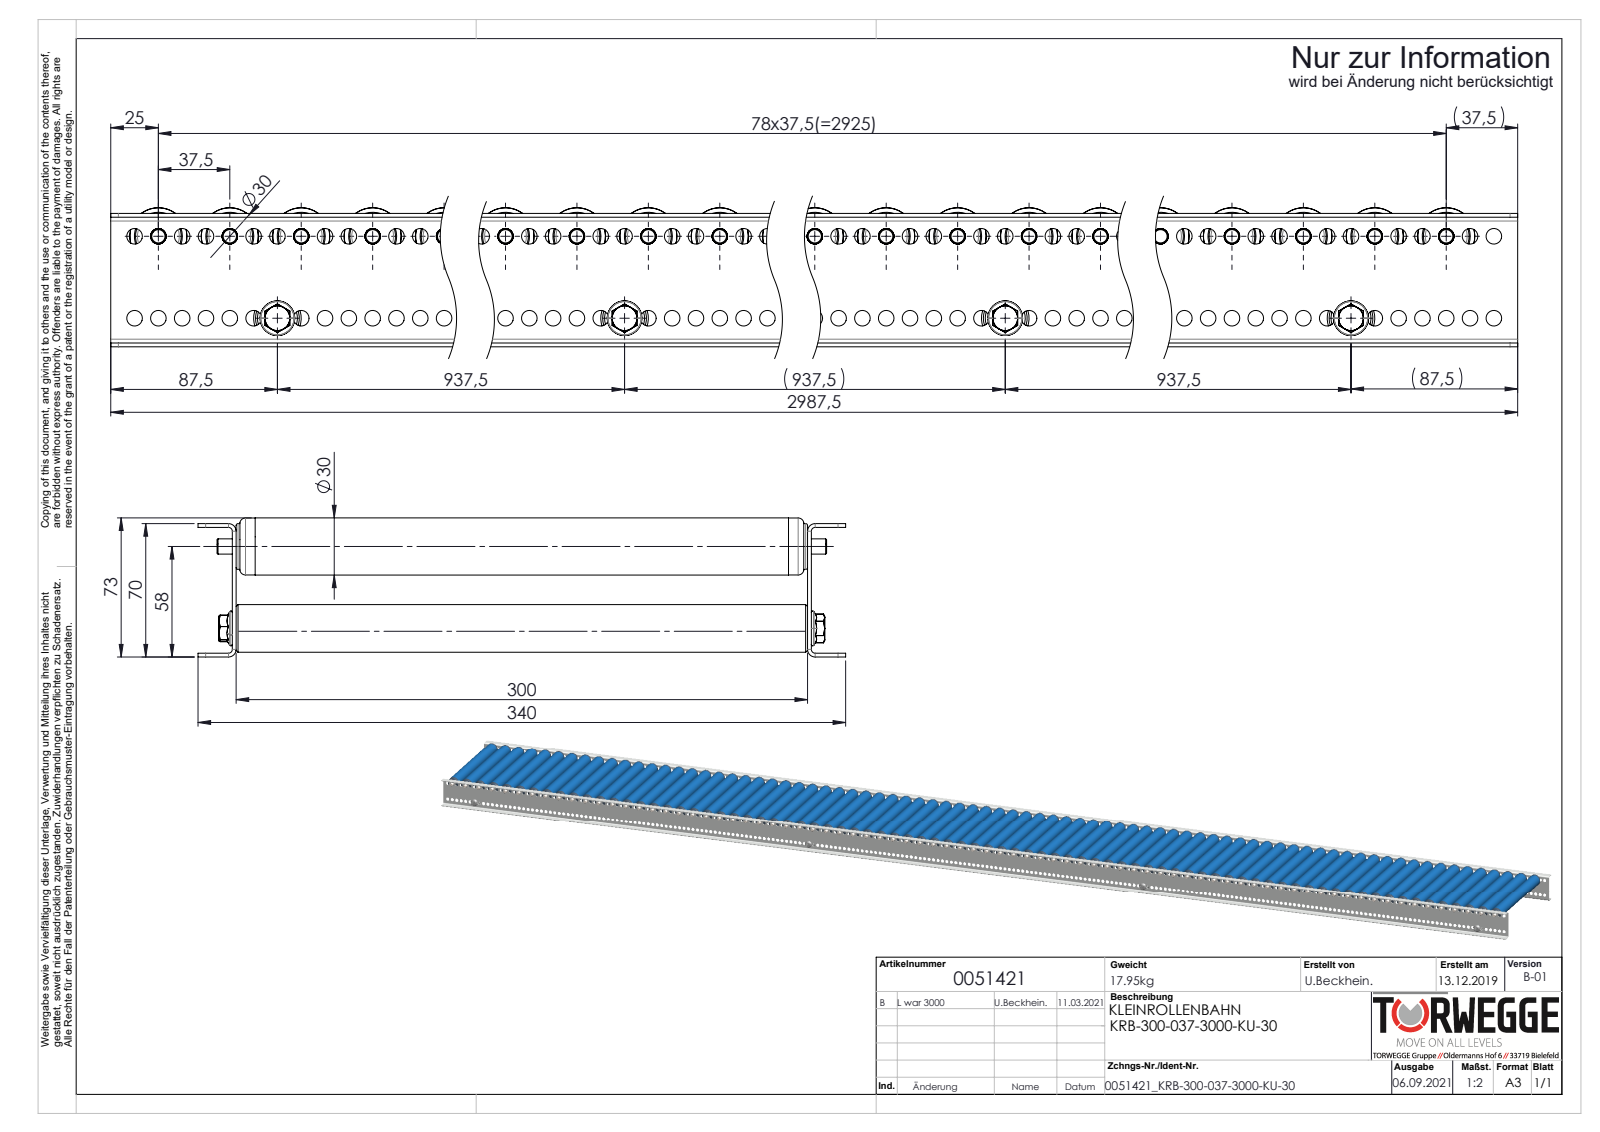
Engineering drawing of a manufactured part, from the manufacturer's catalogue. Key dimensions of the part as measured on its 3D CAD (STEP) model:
Part name (STEP PRODUCT): S100995_TYP-KUT50-30x1,8-A8; 0017013_Tragrollenrohr-Ø30x1,8KU_KFG_0017012_L=280; KUT50-30x1,8-KB-A8-FA_KFG_0034505TWG_KUT50-30x1,8-KB-A8-FA-EL=300; Profil_KRB-20x70x20x2_KFG_S109079_U-PROFIL-20-70-20-2-KRB-30-L=2987,5 (+4 more)
STEP written by: SolidWorks 2020 (AUTOMOTIVE_DESIGN)
Units: millimetres
Bodies: 180 solids, 18686 faces (5734 planar, 7056 cylindrical, 5896 other)
Overall size (bounding box): 2987.5 × 340 × 73
Volume: 6 162 000 mm³ · Surface area: 6 915 000 mm²
Round holes (diameter × count): ⌀8.2 ×476, ⌀8.1 ×79, ⌀22.6 ×79, ⌀25.2 ×79, ⌀6.8 ×4, ⌀21 ×4
Round bosses / shafts (diameter × count): ⌀8 ×83, ⌀30 ×79, ⌀29.9 ×79, ⌀26.5 ×79, ⌀26.4 ×79, ⌀24 ×79, ⌀25 ×4
Partial cylindrical surfaces — rounded edges, fillets, slot ends (radius × count): R5.05 ×79, R4 ×8, R2 ×4
Main face-to-face distances: 2, 302, 68, 300, 304, 70, 66, 10, 290, 12
Hole centre spacings: 12.5, 25, 37.5, 50, 62.5, 75, 87.5, 100
